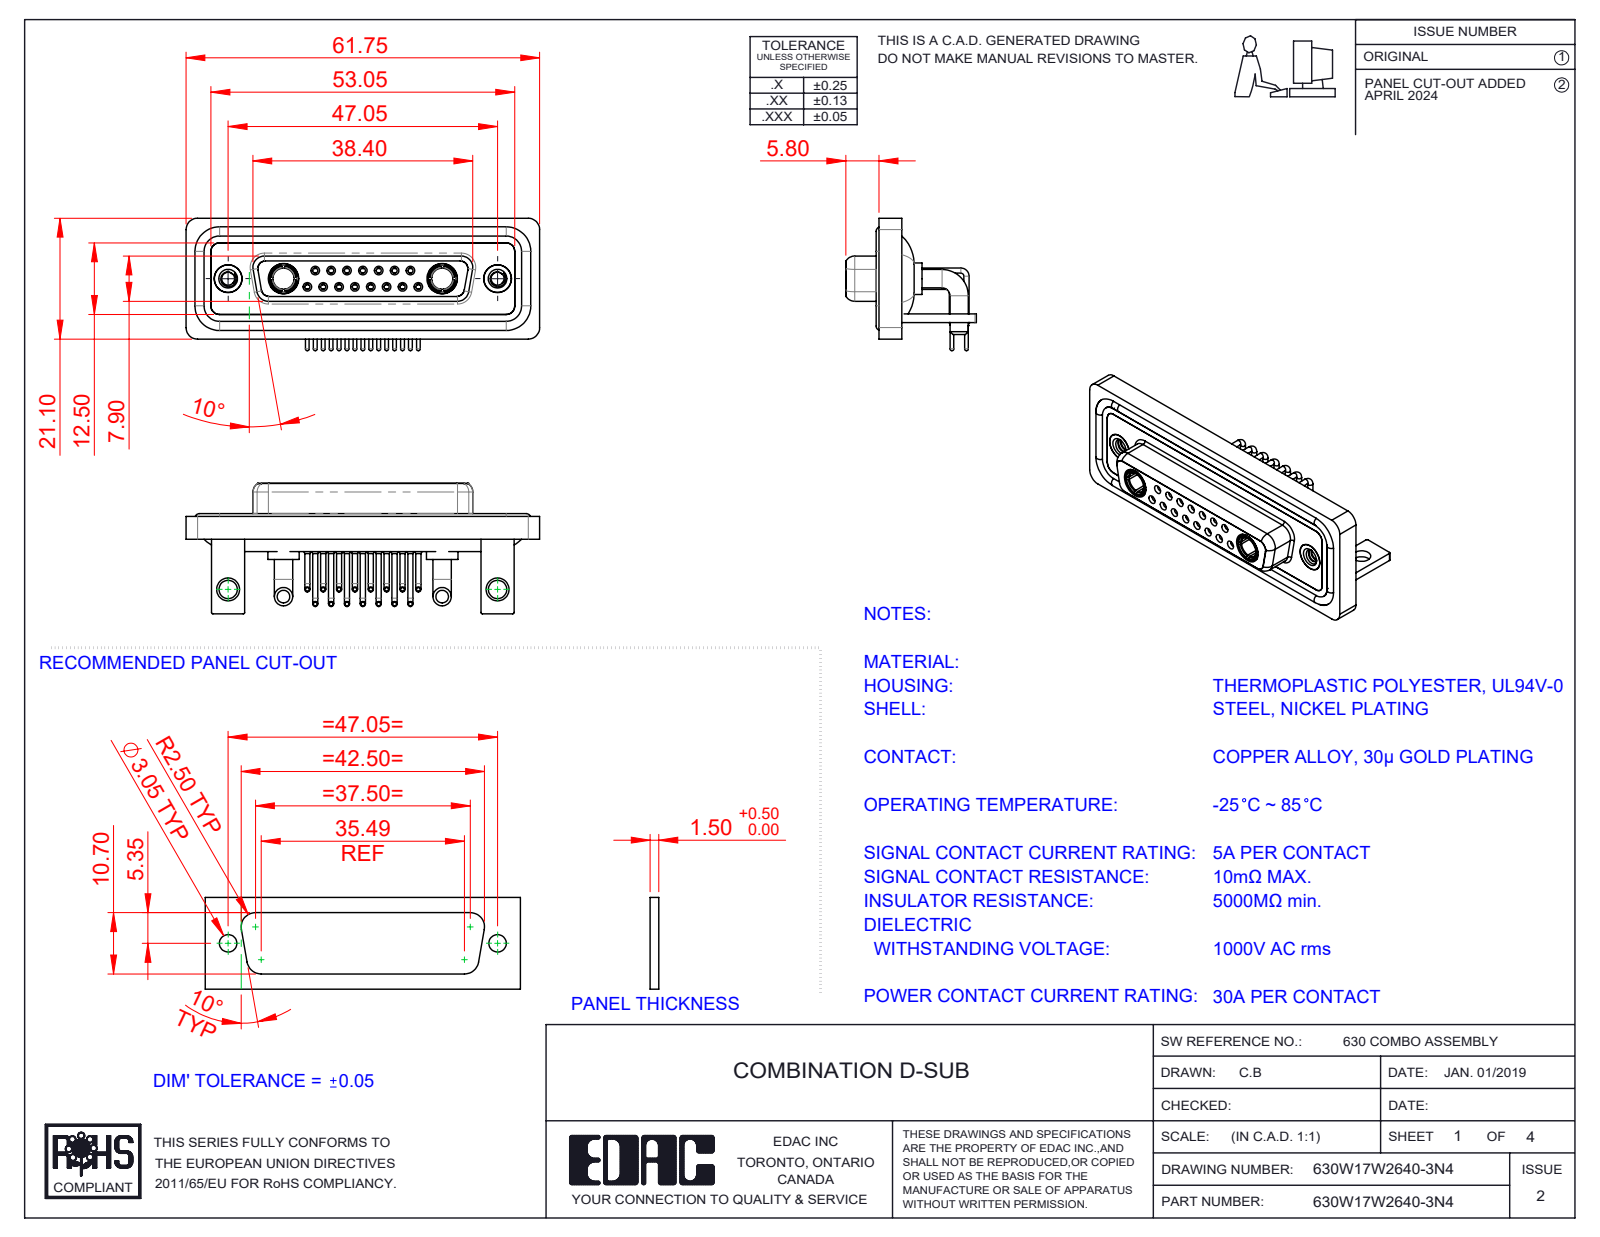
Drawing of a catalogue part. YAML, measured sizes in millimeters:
part_name: "630W17W2640-3N4; 630Combo Shell Front_25 Contacts; 630Combo Stabilizer Bracket_50 Contacts; 630Combo Shell Rear_25 Contacts (+6 more)"
step_written_by: "SolidWorks 2023 (CONFIG_CONTROL_DESIGN)"
units: millimeters
bodies: {solids: 28, faces: 1385, planar: 408, cylindrical: 607, other: 370}
overall_size: [61.75, 23.12, 22.8]
volume: 8909
surface_area: 15302
round_holes:
  - {diameter: 0.9, count: 15}
  - {diameter: 1.1, count: 15}
  - {diameter: 1.5, count: 15}
  - {diameter: 2, count: 15}
  - {diameter: 1.6, count: 8}
  - {diameter: 1.7, count: 7}
  - {diameter: 4.85, count: 4}
  - {diameter: 2.26, count: 2}
  - {diameter: 3.2, count: 2}
  - {diameter: 3.7, count: 2}
  - {diameter: 4, count: 2}
  - {diameter: 4.05, count: 2}
round_bosses_or_shafts:
  - {diameter: 0.9, count: 15}
  - {diameter: 0.65, count: 15}
  - {diameter: 1.6, count: 11}
  - {diameter: 3.2, count: 4}
  - {diameter: 5.5, count: 2}
  - {diameter: 5.2, count: 2}
  - {diameter: 4.96, count: 2}
  - {diameter: 4.95, count: 2}
partial_cylinders:
  - {radius: 2, count: 19}
  - {radius: 1.5, count: 18}
  - {radius: 0.25, count: 16}
  - {radius: 1.35, count: 8}
  - {radius: 1.6, count: 8}
  - {radius: 0.5, count: 5}
  - {radius: 0.6, count: 4}
  - {radius: 0.65, count: 4}
face_to_face_distances: [0.4, 1.8, 2.9, 3.7, 1.5, 4.1, 1.1, 1.4, 1.6, 3.1]
hole_center_spacings: [3.16, 2.77, 5.54, 8.31, 5.04, 7.49, 11.08, 5.03]
